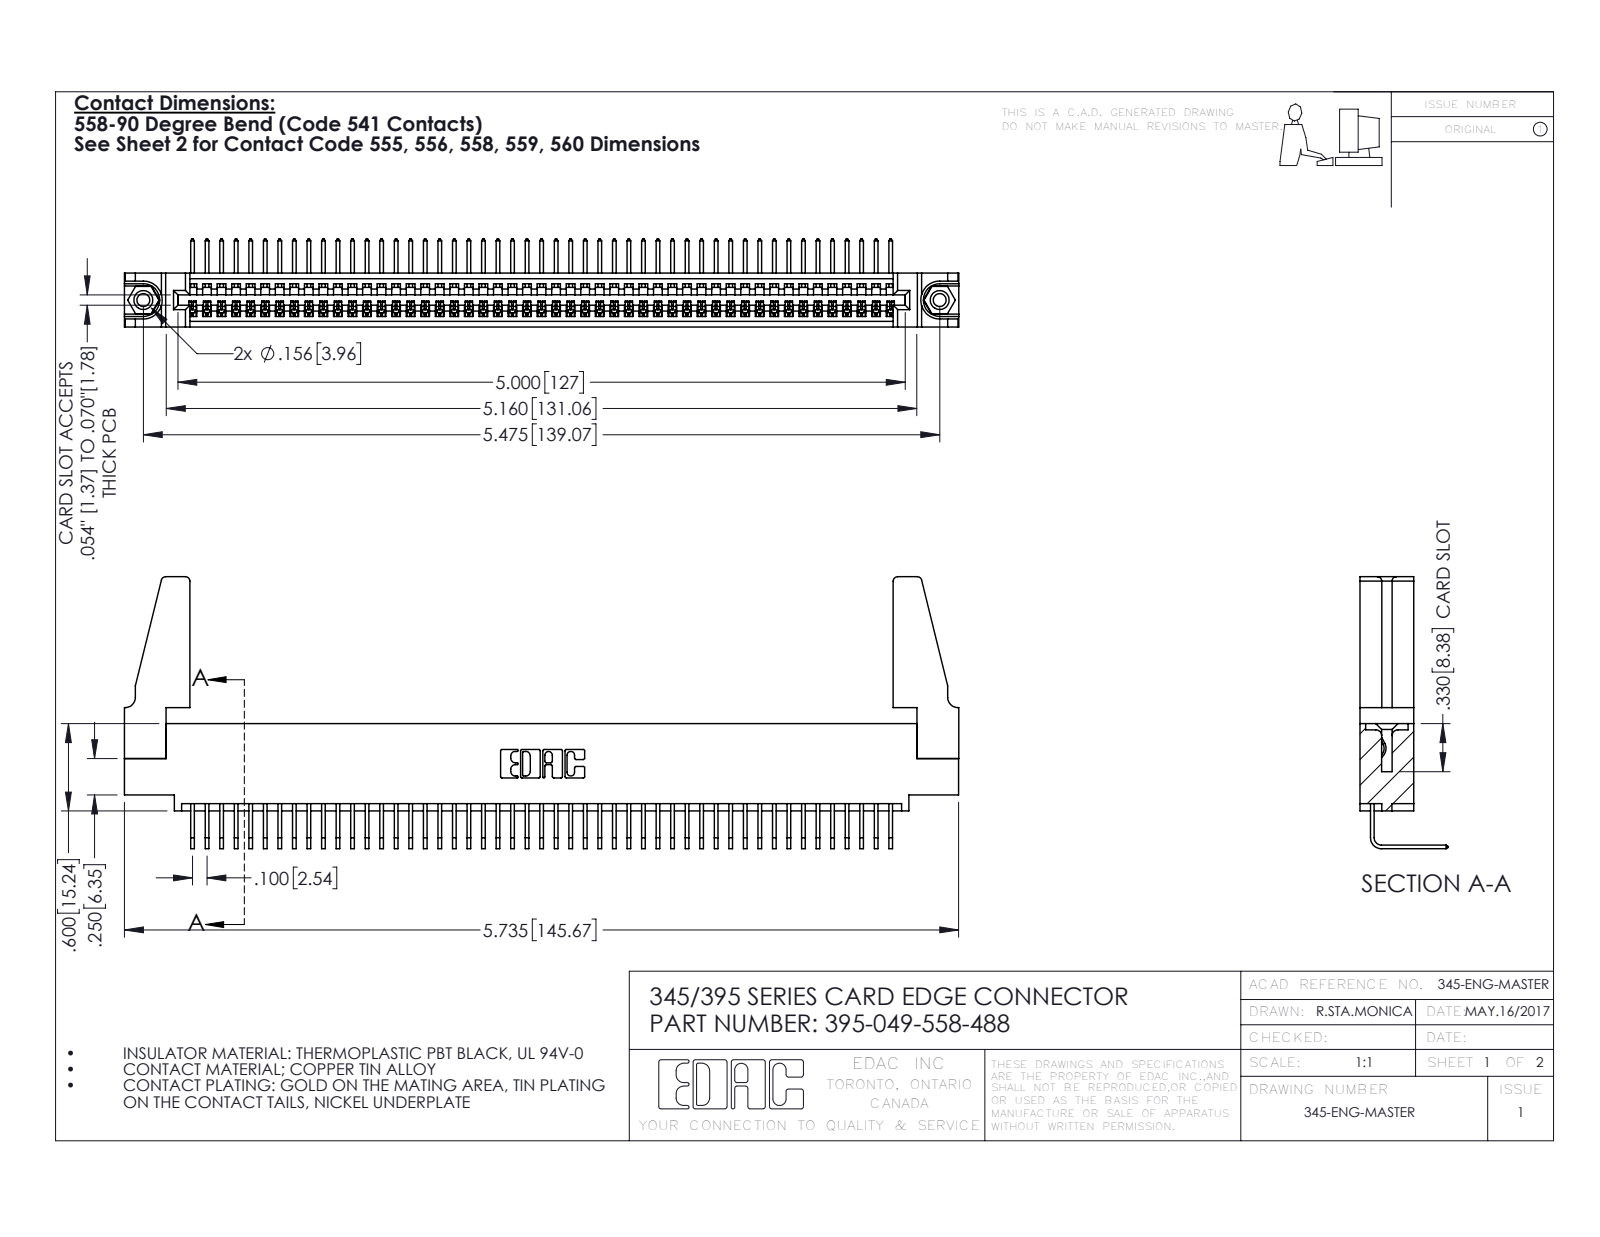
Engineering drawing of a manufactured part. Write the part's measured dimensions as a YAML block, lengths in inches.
part_name: "345-292-001_558 Tail - 2; 345-220-078_345-220-088; 345 Part_0.110 Offset - 0.156 Dia-TH; 345-250-001_345-250-001-102 (+1 more)"
step_written_by: "SolidWorks 2016 (CONFIG_CONTROL_DESIGN)"
units: inches
bodies: {solids: 54, faces: 3194, planar: 2214, cylindrical: 964, other: 16}
overall_size: [5.736, 1.869, 0.605]
volume: 1.052
surface_area: 35.42
round_holes:
  - {diameter: 0.089, count: 2}
  - {diameter: 0.125, count: 2}
  - {diameter: 0.156, count: 2}
  - {diameter: 0.064, count: 1}
round_bosses_or_shafts:
  - {diameter: 0.155, count: 2}
partial_cylinders:
  - {radius: 0.006, count: 98}
  - {radius: 0.01, count: 22}
  - {radius: 0.03, count: 8}
  - {radius: 0.007, count: 6}
  - {radius: 0.031, count: 6}
  - {radius: 0.026, count: 3}
  - {radius: 0.031, count: 2}
  - {radius: 0.04, count: 2}
face_to_face_distances: [0.072, 0.298, 0.37, 0.2, 0.098, 0.272, 0.025, 0.225, 0.149, 0.072]
hole_center_spacings: [0.27, 5.239, 5.475]
